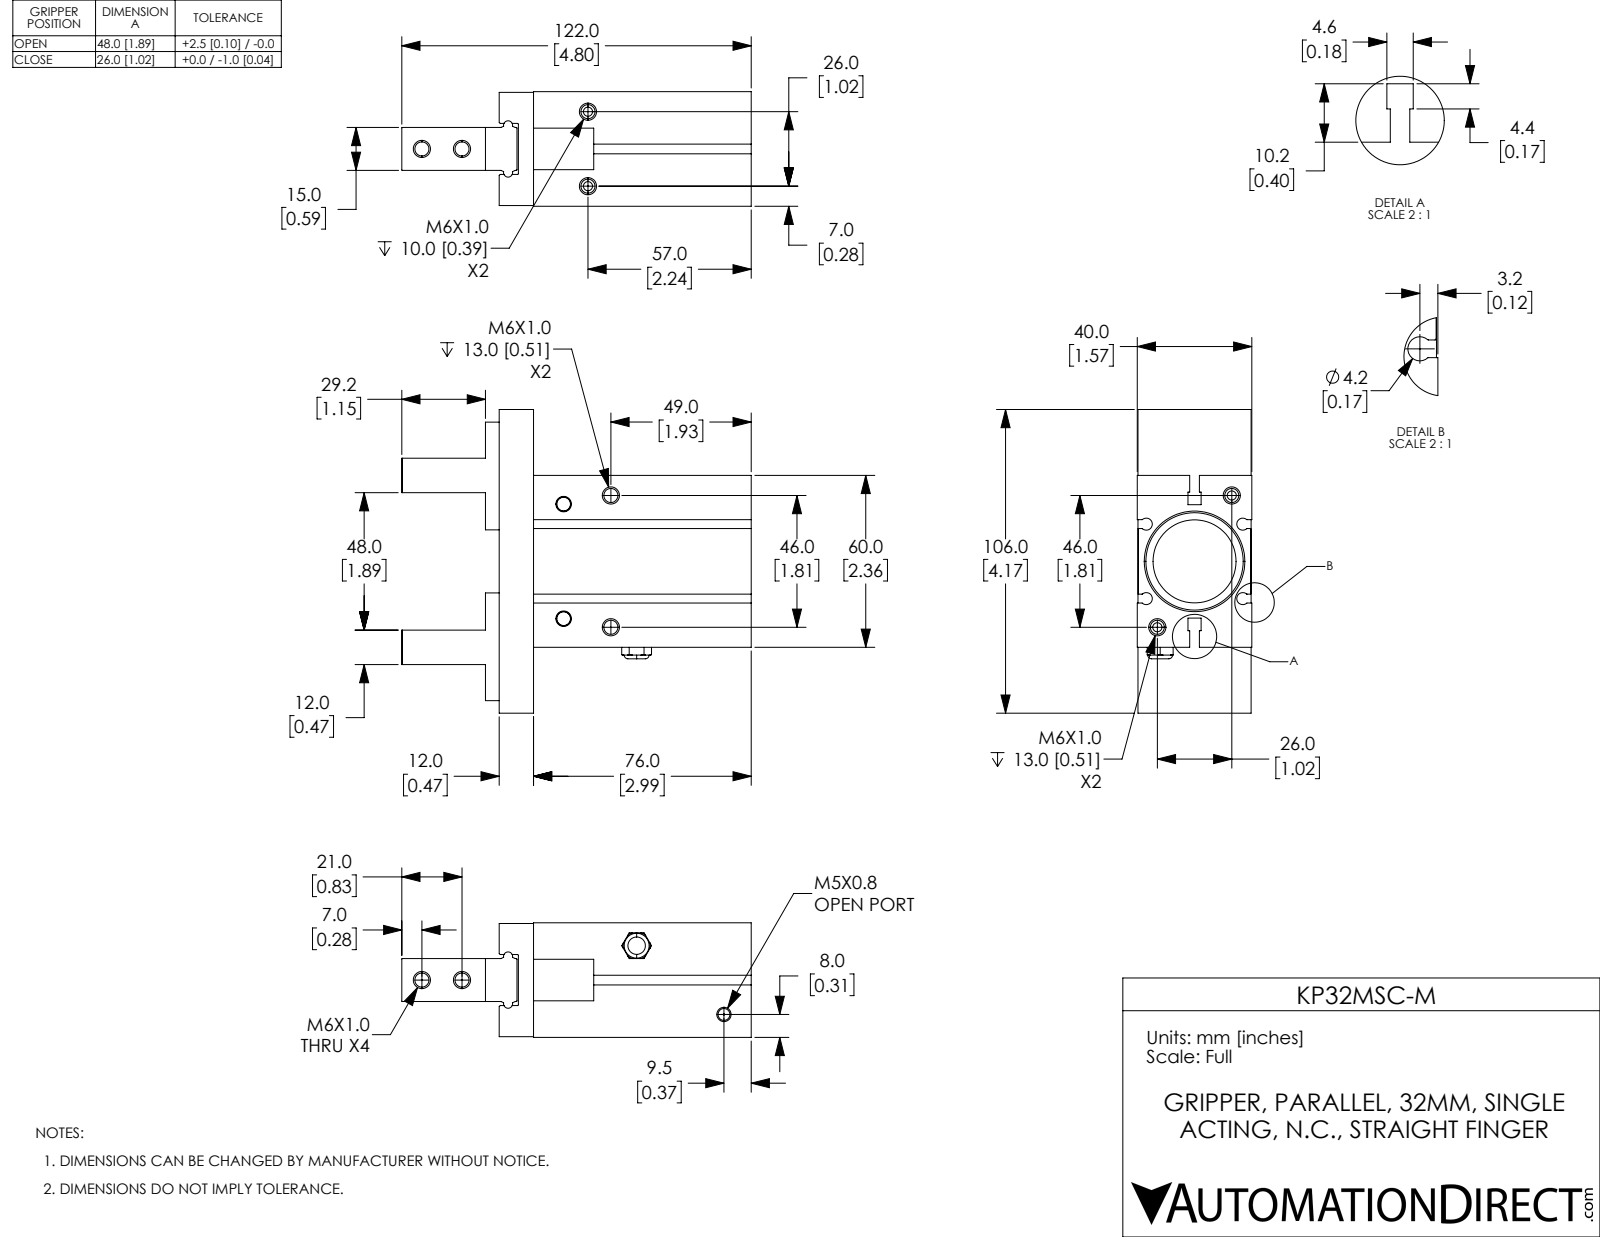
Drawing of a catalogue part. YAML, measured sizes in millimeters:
part_name: "KP32MSC-M; KP32MSC-M-3; KP32MSC-M-2; KP32MSC-M-1"
step_written_by: "SolidWorks 2017 (CONFIG_CONTROL_DESIGN)"
units: millimeters
bodies: {solids: 3, faces: 261, planar: 127, cylindrical: 64, other: 70}
overall_size: [122, 106, 40]
volume: 207512
surface_area: 48459
round_holes:
  - {diameter: 4.92, count: 4}
  - {diameter: 4.92, count: 4}
  - {diameter: 0.5, count: 2}
  - {diameter: 4.13, count: 2}
  - {diameter: 6.02, count: 2}
  - {diameter: 6.1, count: 1}
  - {diameter: 29, count: 1}
  - {diameter: 34, count: 1}
partial_cylinders:
  - {radius: 0.2, count: 6}
  - {radius: 2.1, count: 4}
  - {radius: 0.3, count: 2}
  - {radius: 1.59, count: 2}
face_to_face_distances: [12.5, 27.25, 39.7, 12.75, 39.75, 39.45, 27, 12.45, 26.95, 60]
hole_center_spacings: [26.42, 45.88, 59.44, 14, 17.03, 26, 30.23, 38.81]
